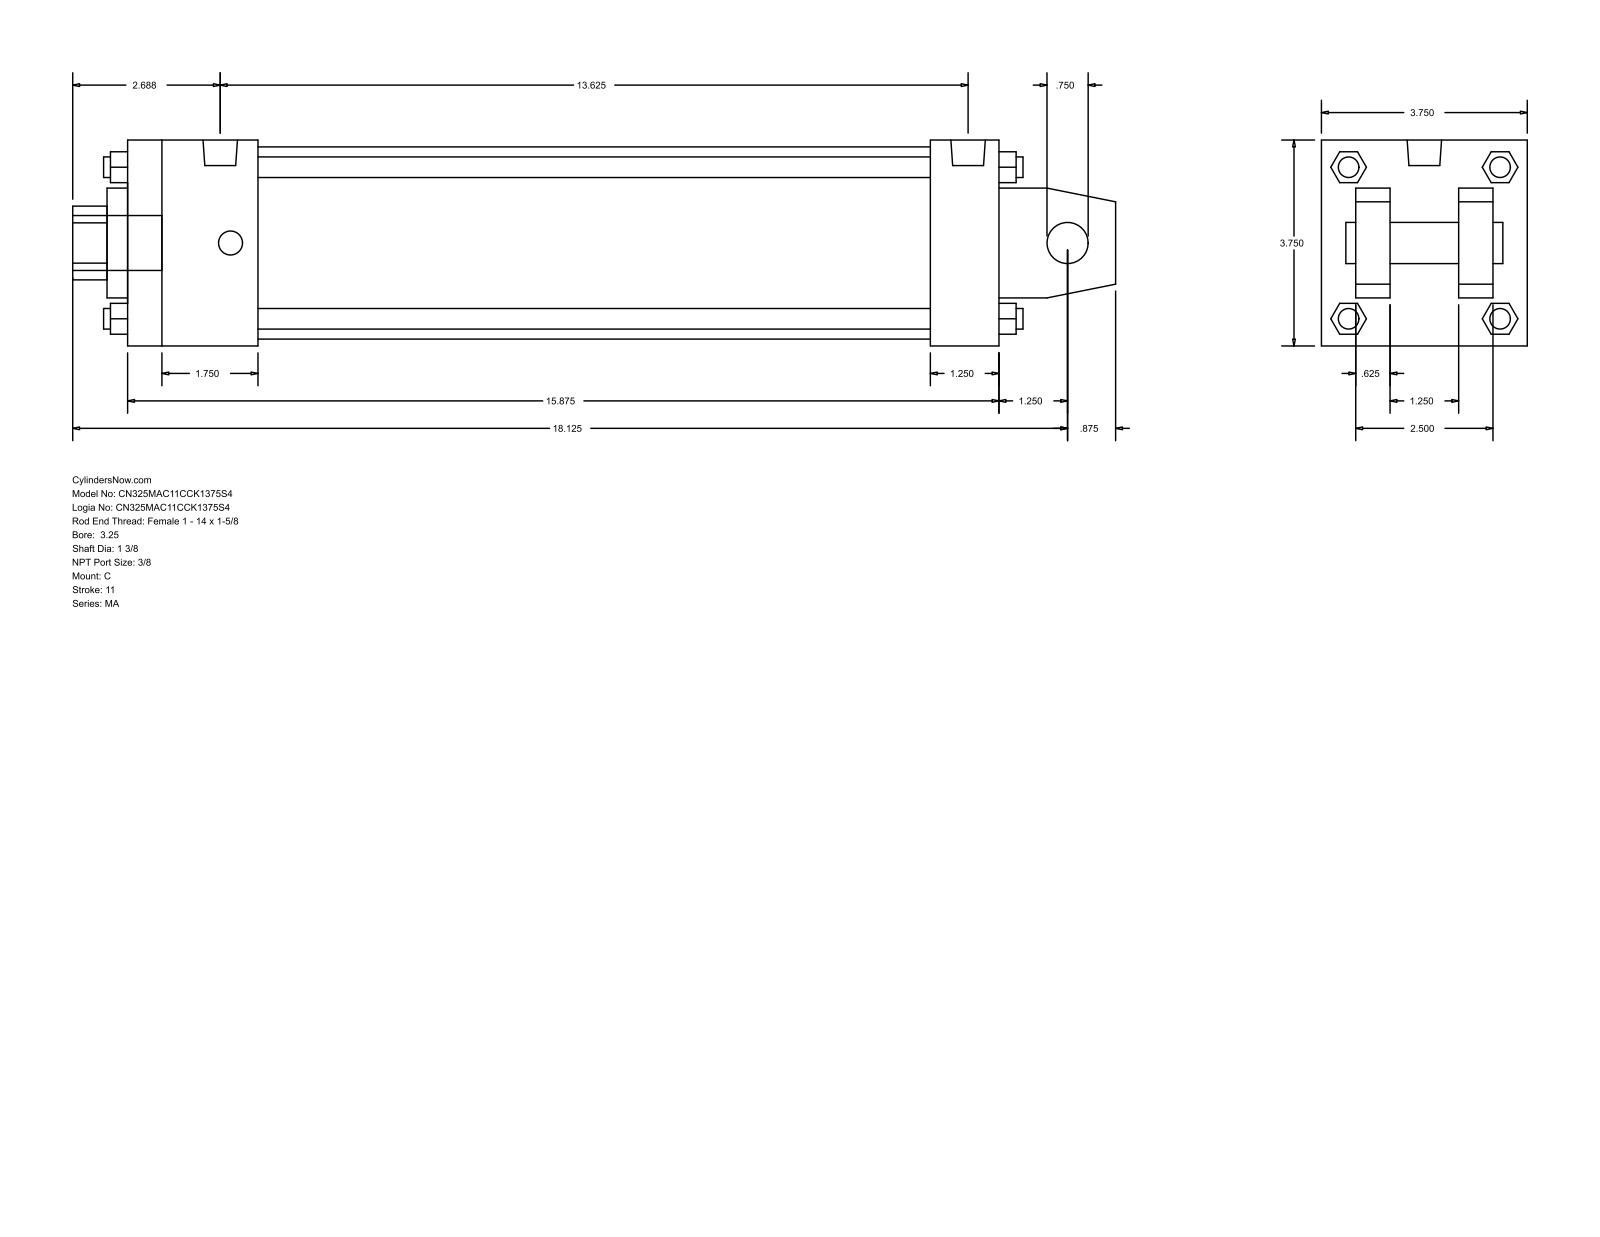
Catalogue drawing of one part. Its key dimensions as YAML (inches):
part_name: "MA_C__0325_1.375"
step_written_by: "GSSL Pune (CONFIG_CONTROL_DESIGN)"
units: inches
bodies: {solids: 0, faces: 139, planar: 108, cylindrical: 31, other: 0}
overall_size: [19, 3.75, 3.75]
round_holes:
  - {diameter: 0.75, count: 1}
  - {diameter: 1.375, count: 1}
  - {diameter: 2, count: 1}
  - {diameter: 3.5, count: 1}
round_bosses_or_shafts:
  - {diameter: 0.437, count: 4}
  - {diameter: 0.375, count: 4}
  - {diameter: 0.627, count: 2}
  - {diameter: 1, count: 1}
partial_cylinders:
  - {radius: 0.672, count: 1}
face_to_face_distances: [3.75, 0.625, 1.25, 2.5, 15.875, 3.125, 1.875, 14.625, 2.375, 12.25]
